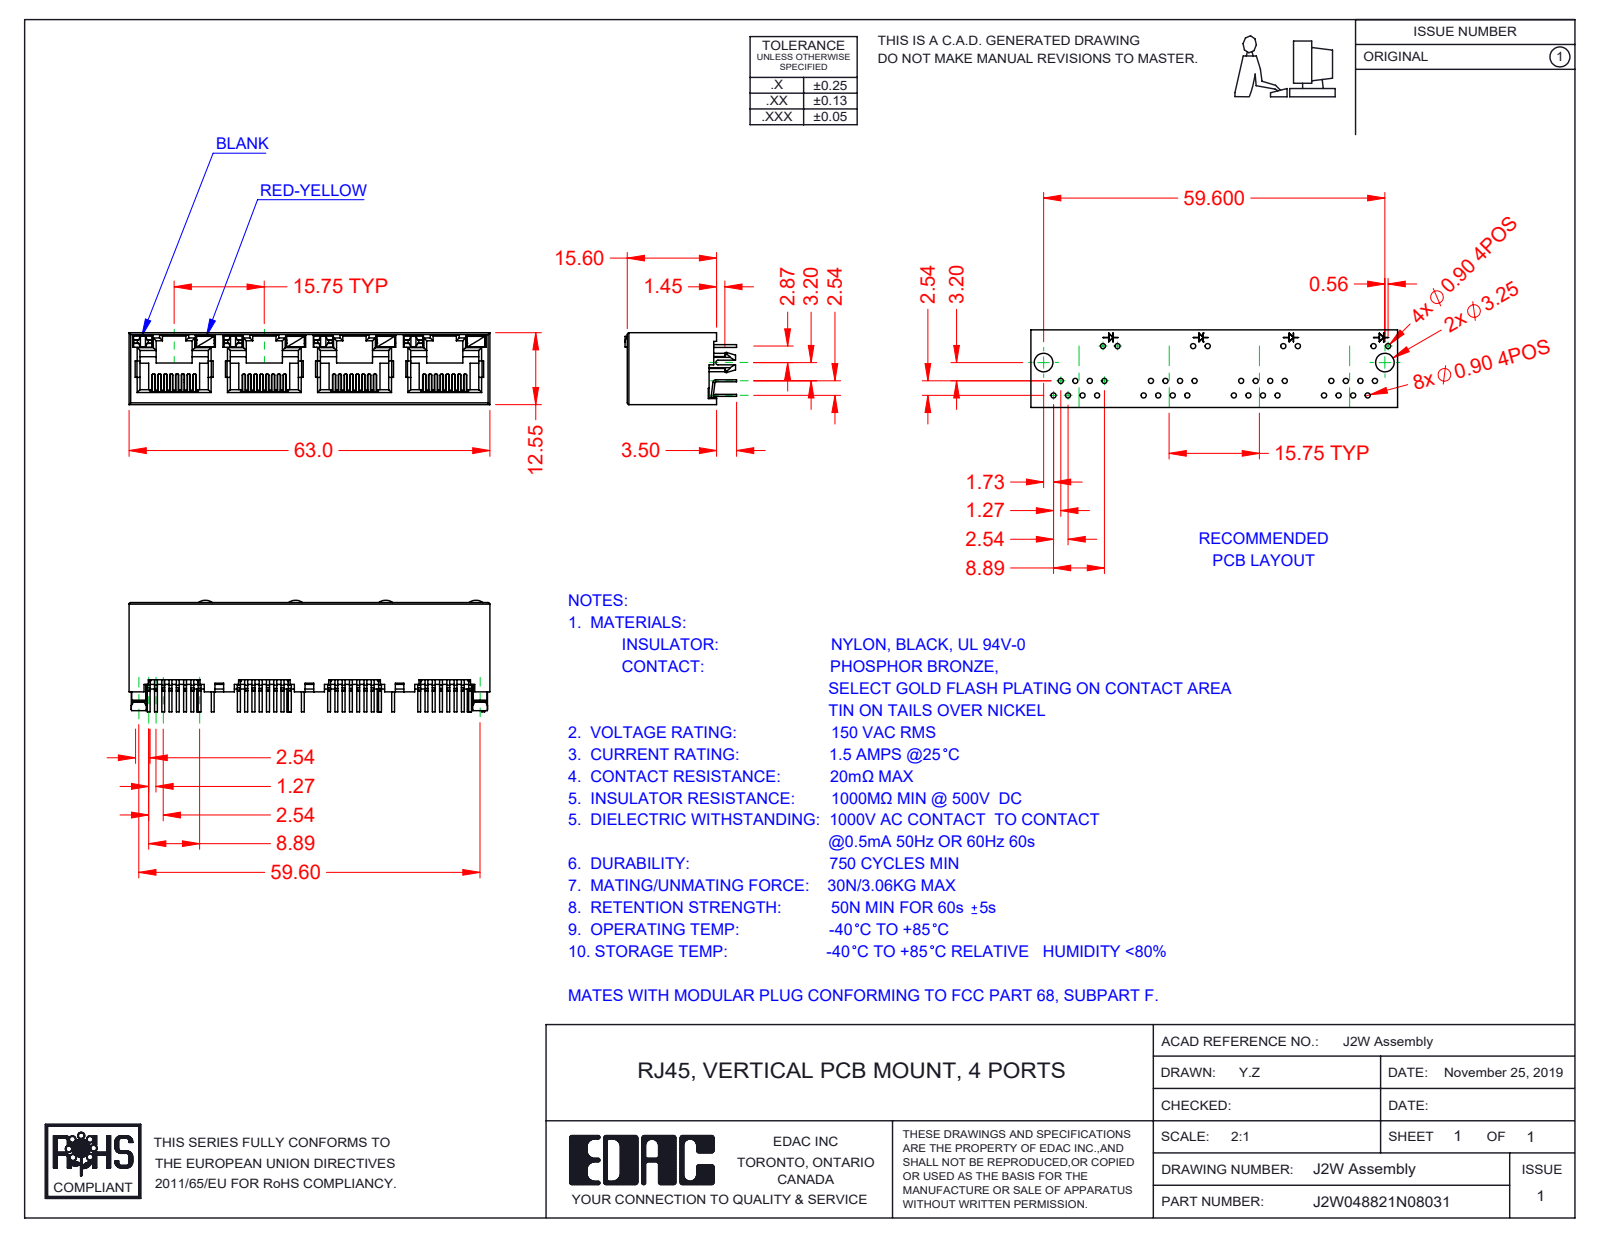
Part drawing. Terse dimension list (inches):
name: 2W LED RH_8-Red-Yellow; 2W Contacts; 2W Insulator; 2W Contact Lock (+2 more)
written by: SolidWorks 2020 (CONFIG_CONTROL_DESIGN)
unit: in
bodies: 41 solids, 3011 faces (2508 planar, 445 cylindrical, 58 other)
size: 2.48 × 0.768 × 0.494
volume: 0.318 in³; area: 19.68 in²
rounds: 64× R0.006, 29× R0.008, 28× R0.02, 14× R0.012, 8× R0.018, 4× R0.079, 2× R0.01, 2× R0.059
face distances: 0.494, 0.469, 0.026, 0.62, 0.014, 0.059, 0.031, 0.024, 0.445, 1.24
